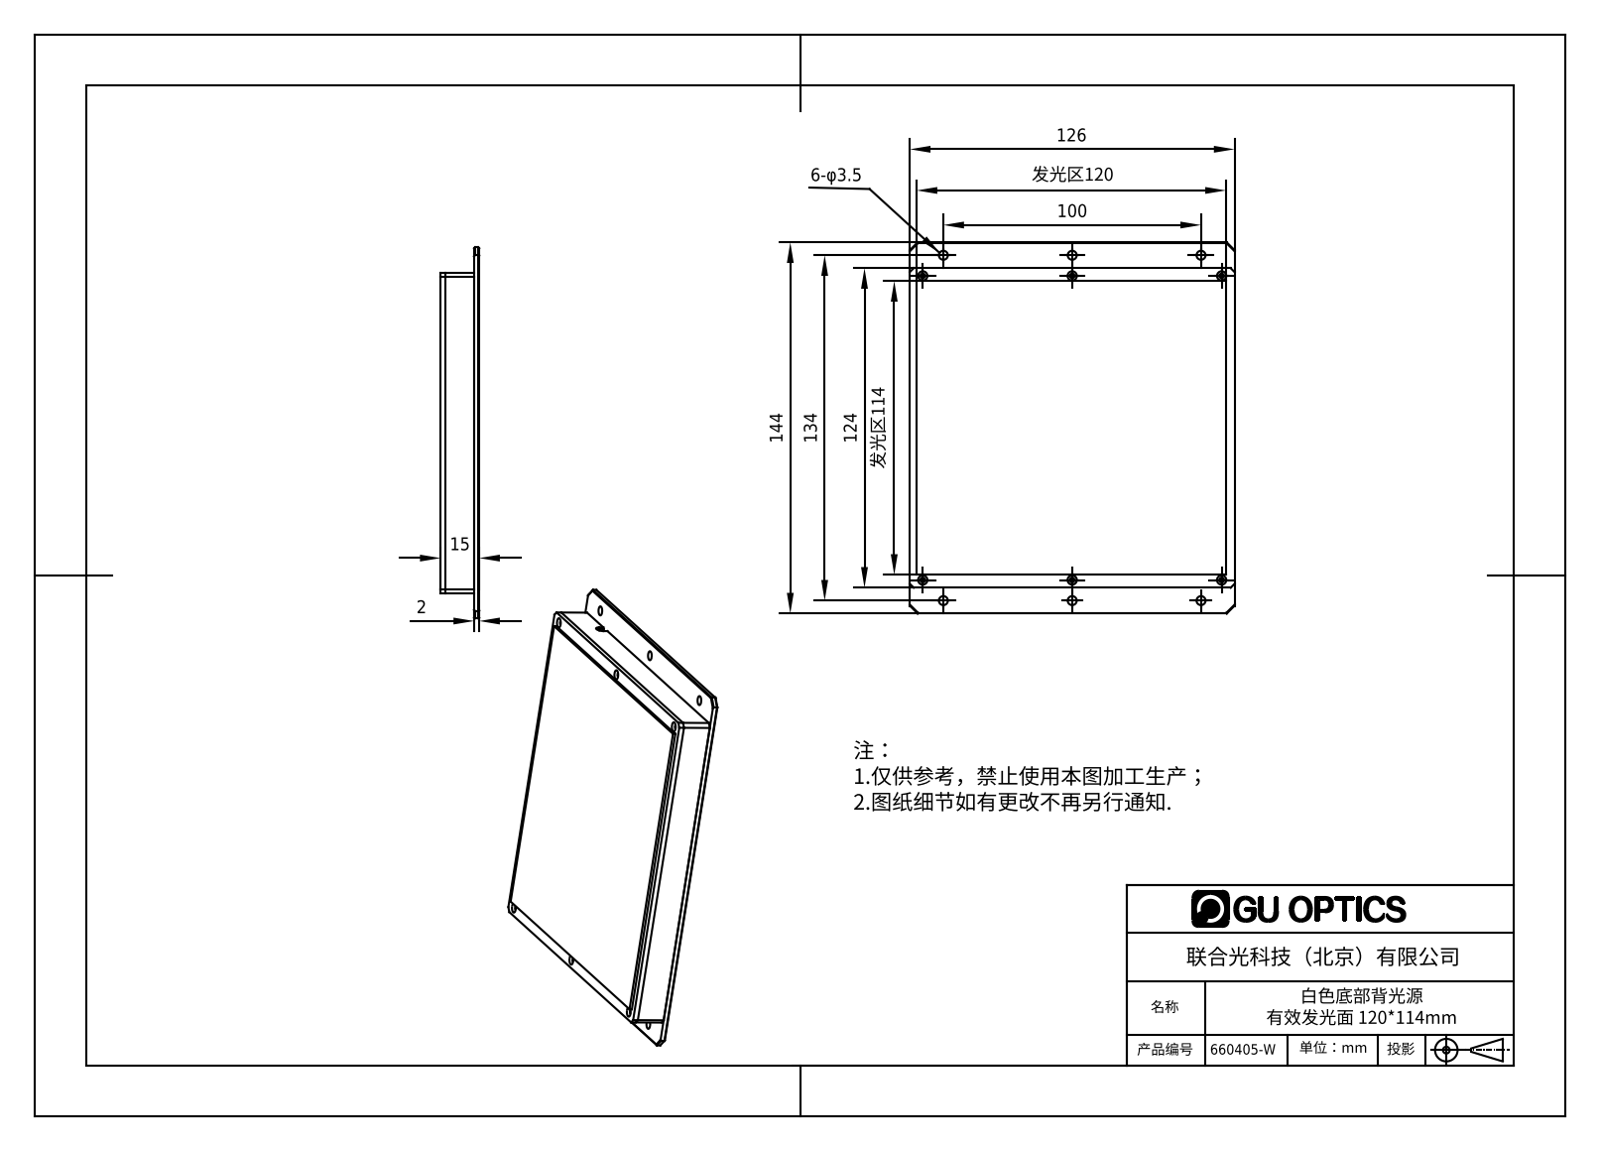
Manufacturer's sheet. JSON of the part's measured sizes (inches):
{"part_name": "660405-W", "step_written_by": "SolidWorks 2016 (AUTOMOTIVE_DESIGN)", "units": "inches", "bodies": {"solids": 4, "faces": 2126, "planar": 1933, "cylindrical": 86, "other": 107}, "overall_size": [5.669, 4.961, 0.63], "volume_in3": 7.033, "surface_area_in2": 176.2, "round_holes": [[0.049, 6], [0.063, 6], [0.071, 6], [0.079, 6], [0.094, 6], [0.138, 6]], "partial_cylinders_radius": [[0.039, 4], [0.059, 4], [0.079, 2], [0.063, 1]], "face_to_face_distances": [0.512, 0.118, 0.079, 0.433, 0.551, 0.63, 0.039, 0.394, 0.513, 0.395], "hole_center_spacings": [2.283, 4.567, 5.194, 0.02, 4.665, 0.432, 0.445, 1.969]}
